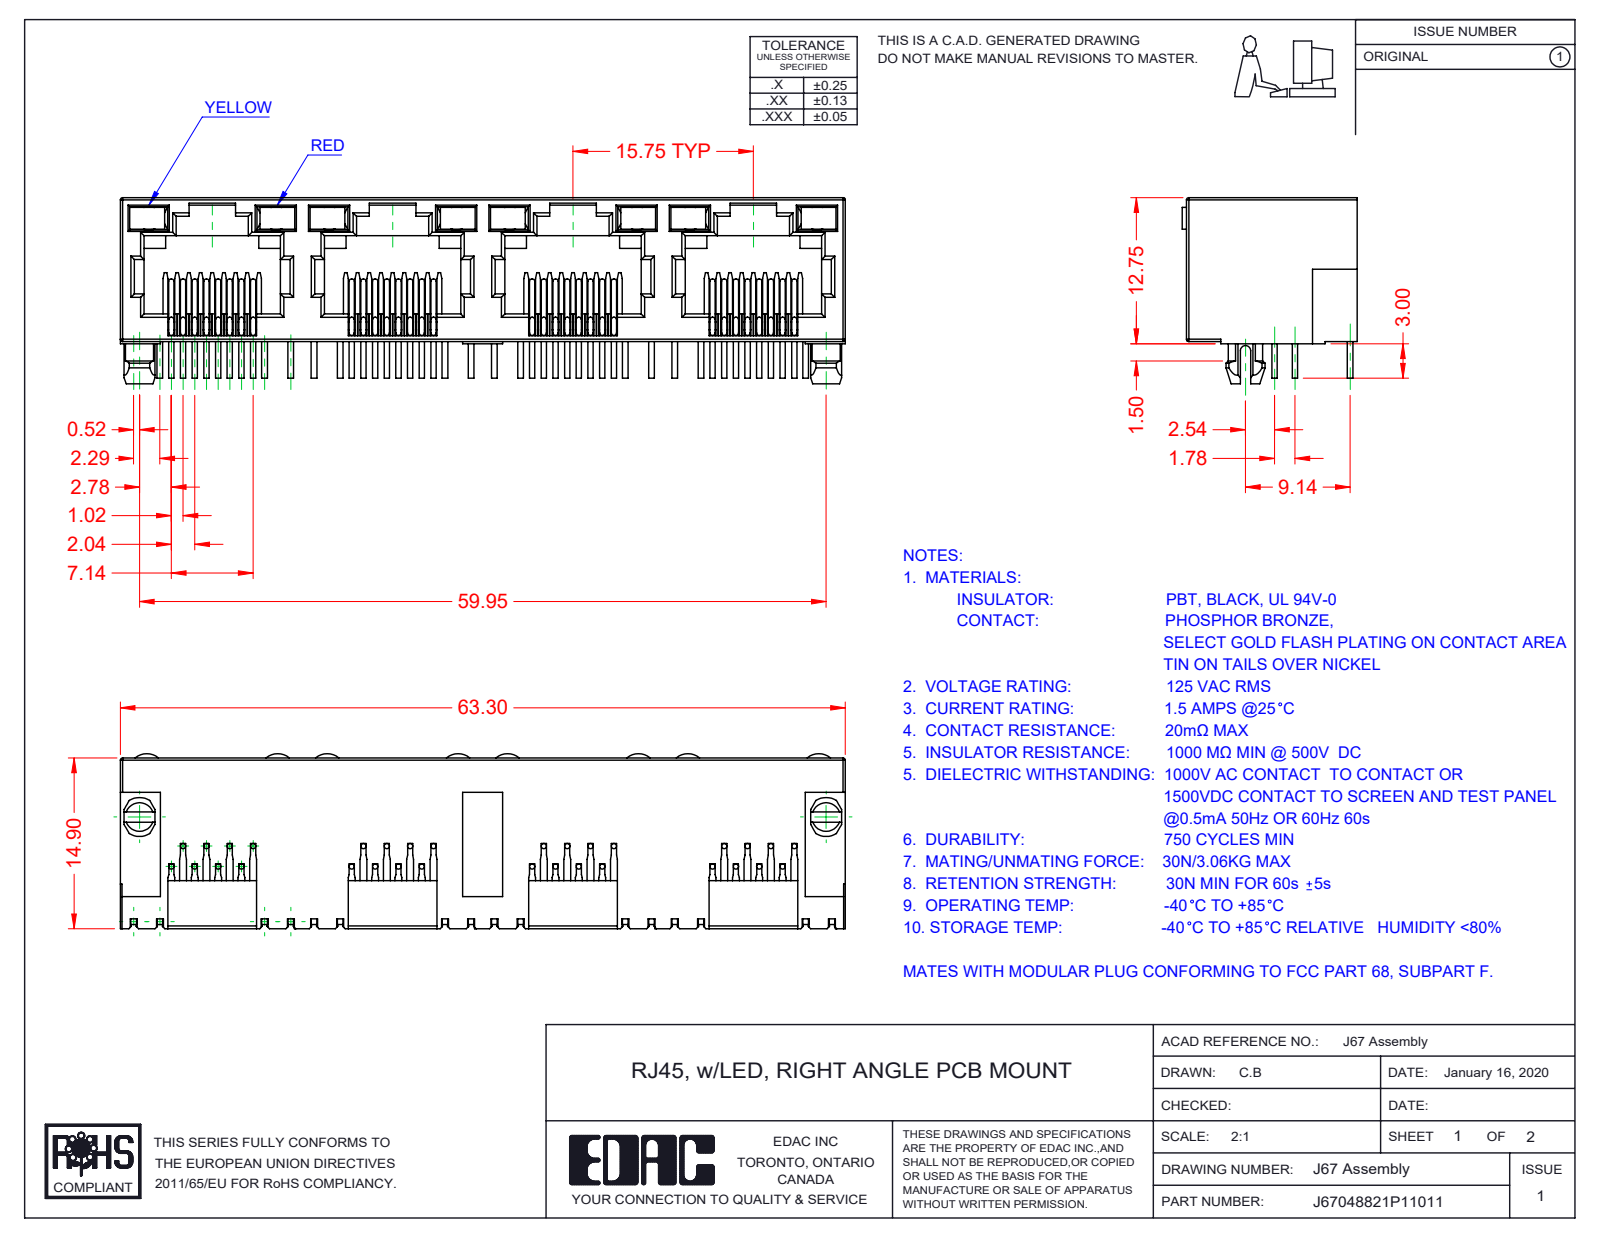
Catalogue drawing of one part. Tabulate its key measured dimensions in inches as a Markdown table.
| quantity | value |
| --- | --- |
| part name | 67 LED RH_2-Red; 67 LED LH_1-Yellow; 67 Contacts; 67 Insulator (+1 more) |
| STEP written by | SolidWorks 2016 (CONFIG_CONTROL_DESIGN) |
| units | inches |
| bodies | 41 solids, 2465 faces (1781 planar, 476 cylindrical, 208 other) |
| overall size | 2.492 × 0.64 × 0.602 |
| volume | 0.315 in³ |
| surface area | 17.94 in² |
| round bosses / shafts (diameter × count) | 0.018 × 96 |
| partial cylindrical surfaces (radius × count) | 0.008 × 66, 0.012 × 29, 0.018 × 9, 0.061 × 8, 0.059 × 2, 0.067 × 2, 0.014 × 1, 0.039 × 1 |
| main face-to-face distances | 0.02, 0.494, 0.074, 0.035, 0.394, 0.62, 0.039, 0.055, 0.433, 0.468 |
